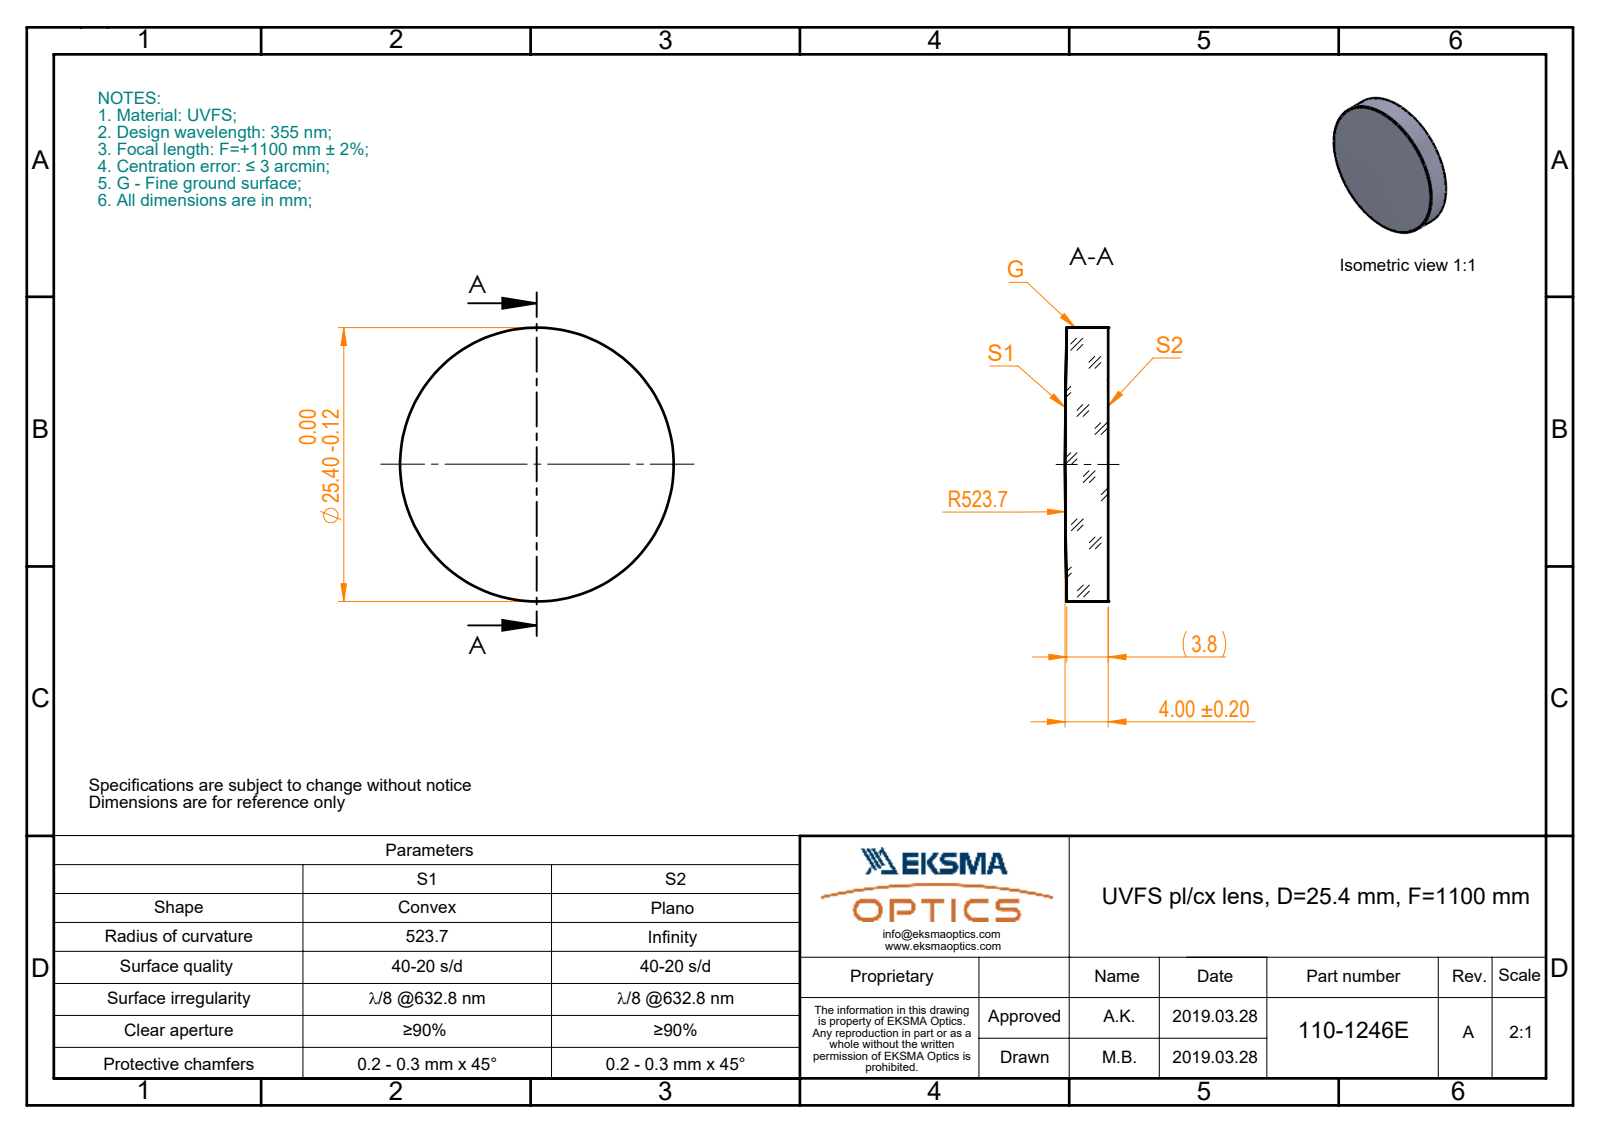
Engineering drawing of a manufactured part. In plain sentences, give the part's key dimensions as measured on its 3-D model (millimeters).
The part is named "110-1246E UVFS pl-cx 25.4 F1100". Its 3-D file was written by "SolidWorks 2017 (CONFIG_CONTROL_DESIGN)". It is 1 solid with 5 faces: 1 planar, 2 cylindrical and 2 other. Overall it measures 25.4 by 25.4 by 4 millimeters. Its volume is 1 988 cubic millimeters and its surface area 1 320 square millimeters. Round bosses or shafts: 1 of diameter 25.4.
